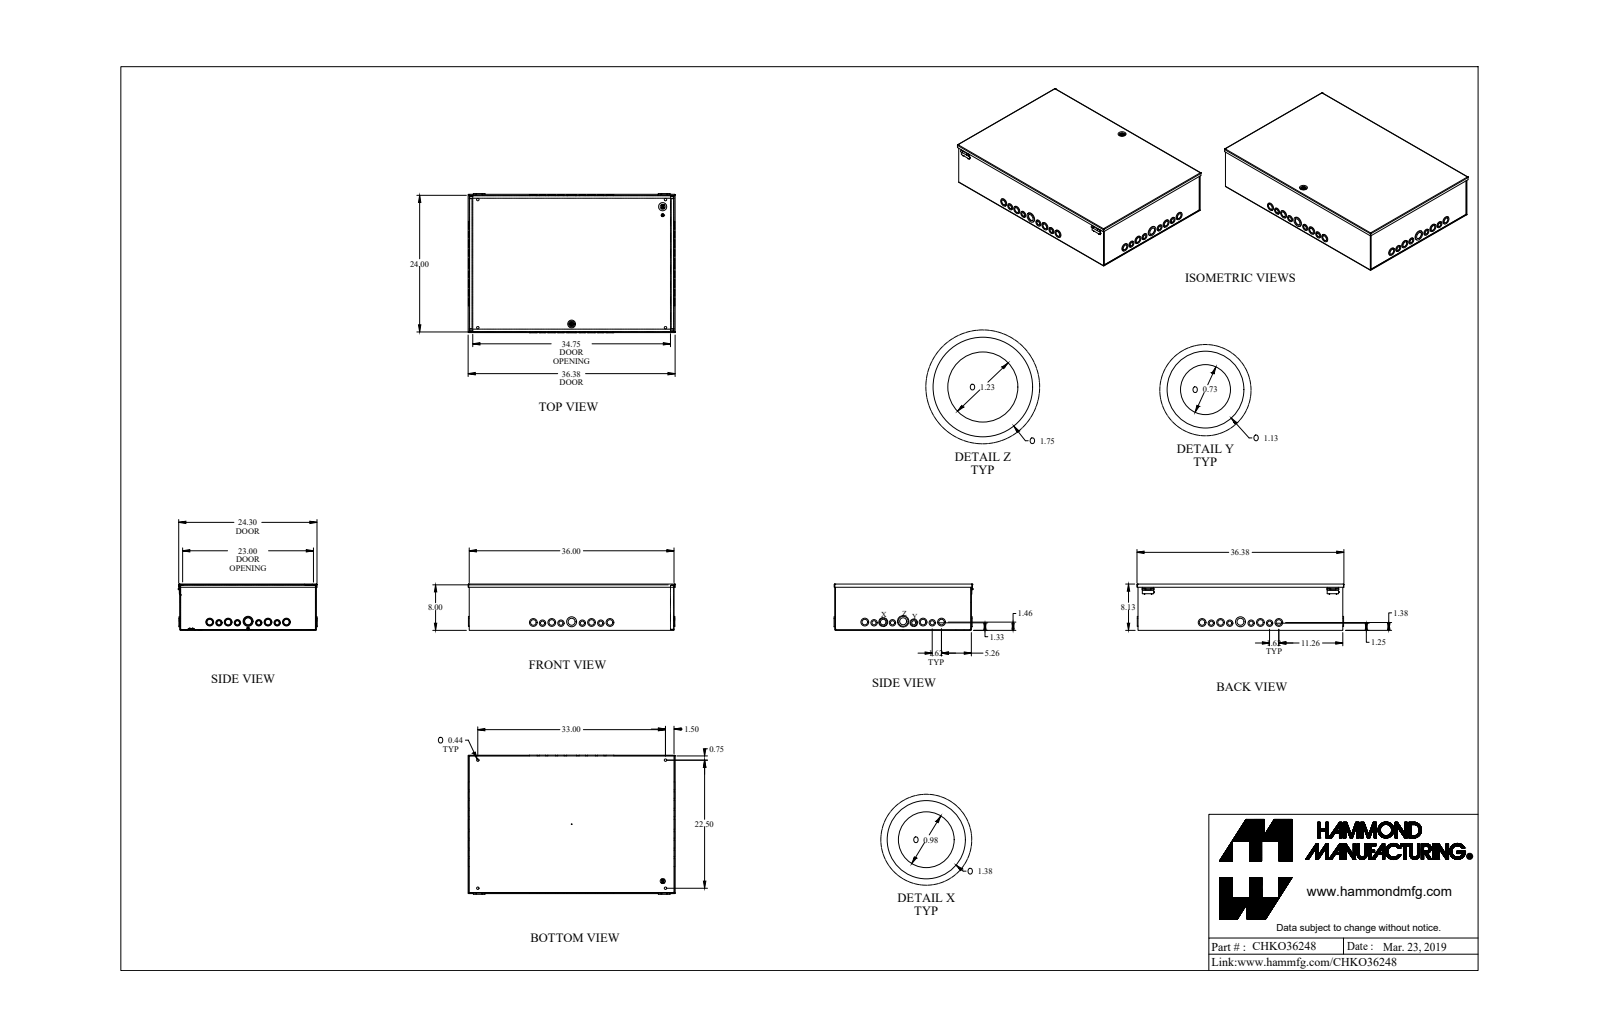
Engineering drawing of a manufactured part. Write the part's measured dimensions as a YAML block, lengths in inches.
part_name: "CHKO36248_Default"
step_written_by: "SolidWorks 2019 (CONFIG_CONTROL_DESIGN)"
units: inches
bodies: {solids: 12, faces: 919, planar: 416, cylindrical: 460, other: 43}
overall_size: [36.375, 24.446, 8.133]
volume: 207
surface_area: 5782
round_holes:
  - {diameter: 0.981, count: 16}
  - {diameter: 1.231, count: 10}
  - {diameter: 0.731, count: 8}
  - {diameter: 0.437, count: 4}
  - {diameter: 1.606, count: 2}
  - {diameter: 0.125, count: 1}
  - {diameter: 0.17, count: 1}
  - {diameter: 0.319, count: 1}
  - {diameter: 0.476, count: 1}
  - {diameter: 0.5, count: 1}
round_bosses_or_shafts:
  - {diameter: 1.125, count: 14}
  - {diameter: 1.375, count: 9}
  - {diameter: 0.875, count: 8}
  - {diameter: 0.131, count: 8}
  - {diameter: 0.875, count: 6}
  - {diameter: 1.125, count: 4}
  - {diameter: 1.375, count: 3}
  - {diameter: 1.75, count: 2}
partial_cylinders:
  - {radius: 0.036, count: 18}
  - {radius: 0.108, count: 16}
  - {radius: 0.072, count: 8}
  - {radius: 0.012, count: 4}
  - {radius: 0.1, count: 4}
  - {radius: 0.079, count: 2}
  - {radius: 0.25, count: 2}
  - {radius: 0.022, count: 1}
face_to_face_distances: [0.072, 8.061, 8.133, 7.989, 23.928, 35.928, 24, 23.856, 36, 35.856]
hole_center_spacings: [1.625, 3.24, 8.621, 7, 10.24, 1.896, 3.502, 4.862]
